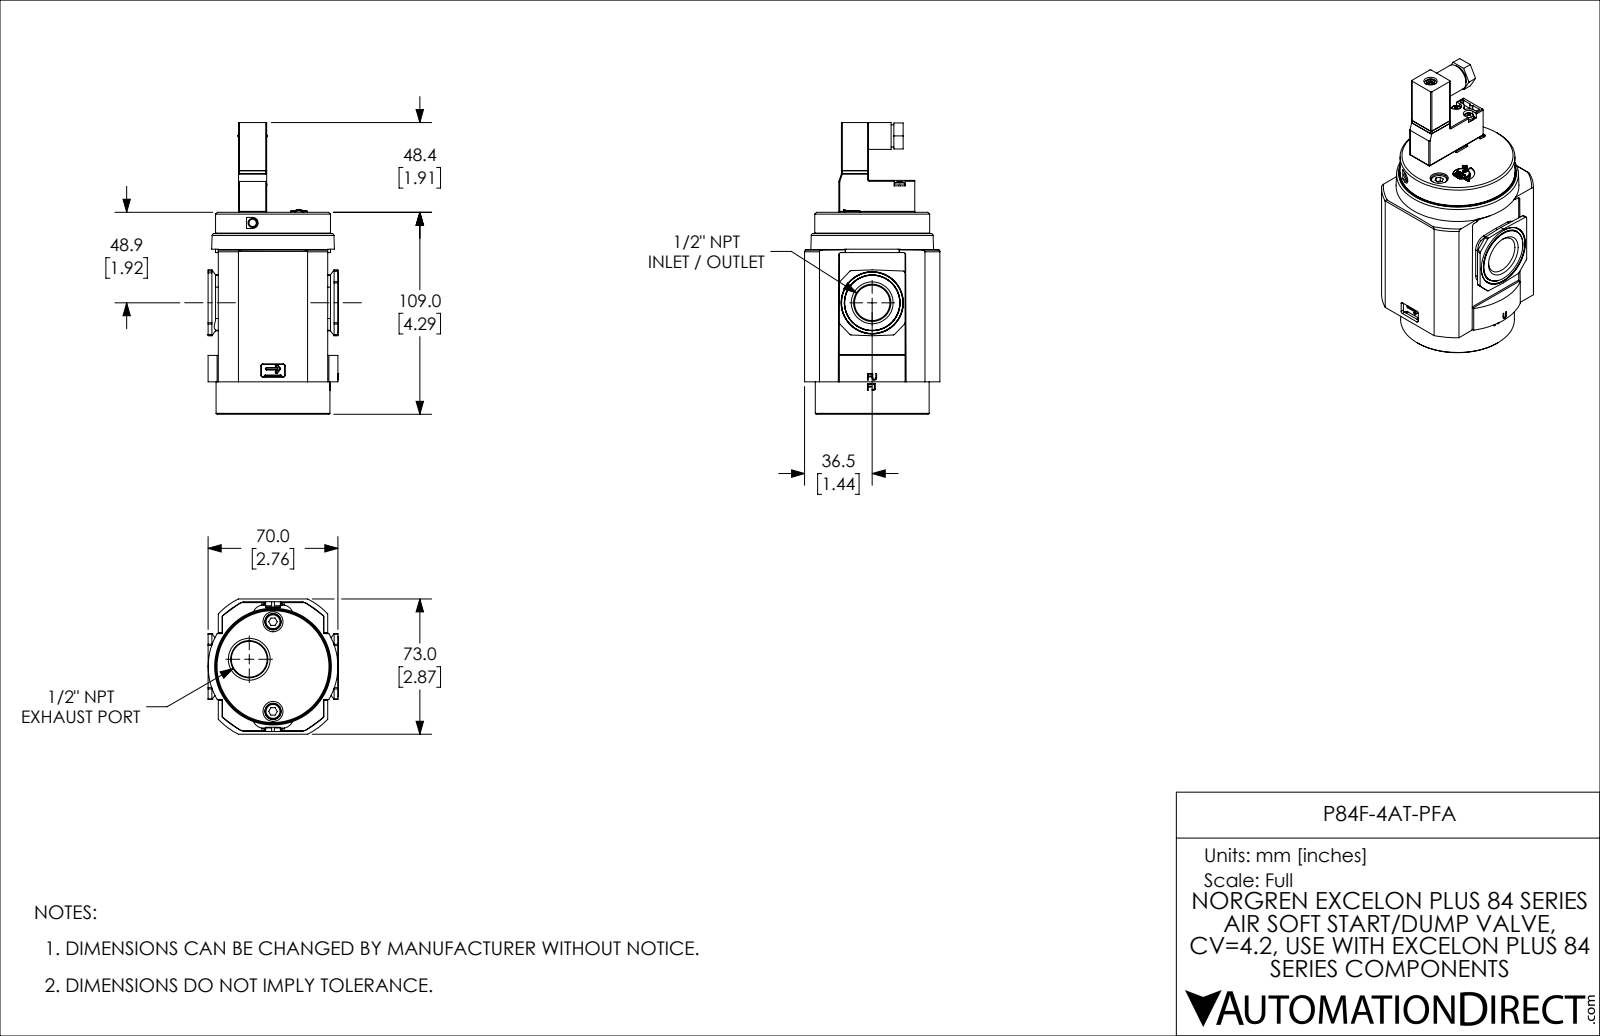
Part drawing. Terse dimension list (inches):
name: P84F-4AT-PFA
written by: SolidWorks 2021 (CONFIG_CONTROL_DESIGN)
unit: in
bodies: 8 solids, 1169 faces (576 planar, 354 cylindrical, 239 other)
size: 6.195 × 2.874 × 2.766
volume: 25.37 in³; area: 151.1 in²
holes: 4× ⌀0.194, 4× ⌀0.209, 4× ⌀0.346, 3× ⌀0.059, 3× ⌀0.097, 2× ⌀0.031, 2× ⌀0.075, 2× ⌀0.122, 2× ⌀0.335, 1× ⌀0.07, 1× ⌀0.118, 1× ⌀0.15
bosses: 4× ⌀0.335, 4× ⌀0.197, 2× ⌀0.118, 1× ⌀2.441, 1× ⌀2.417, 1× ⌀2.323, 1× ⌀0.571, 1× ⌀0.472
rounds: 34× R0.02, 14× R0.01, 13× R0.039, 4× R0.118, 4× R0.236, 4× R0.248, 3× R0.01, 3× R0.013
face distances: 0.059, 2.764, 0.079, 2.795, 2.815, 0.02, 2.736, 2.756, 0.443, 3.207
hole spacings: 0.15, 0.199, 0.213, 0.28, 0.489, 0.829, 0.98, 1.841
